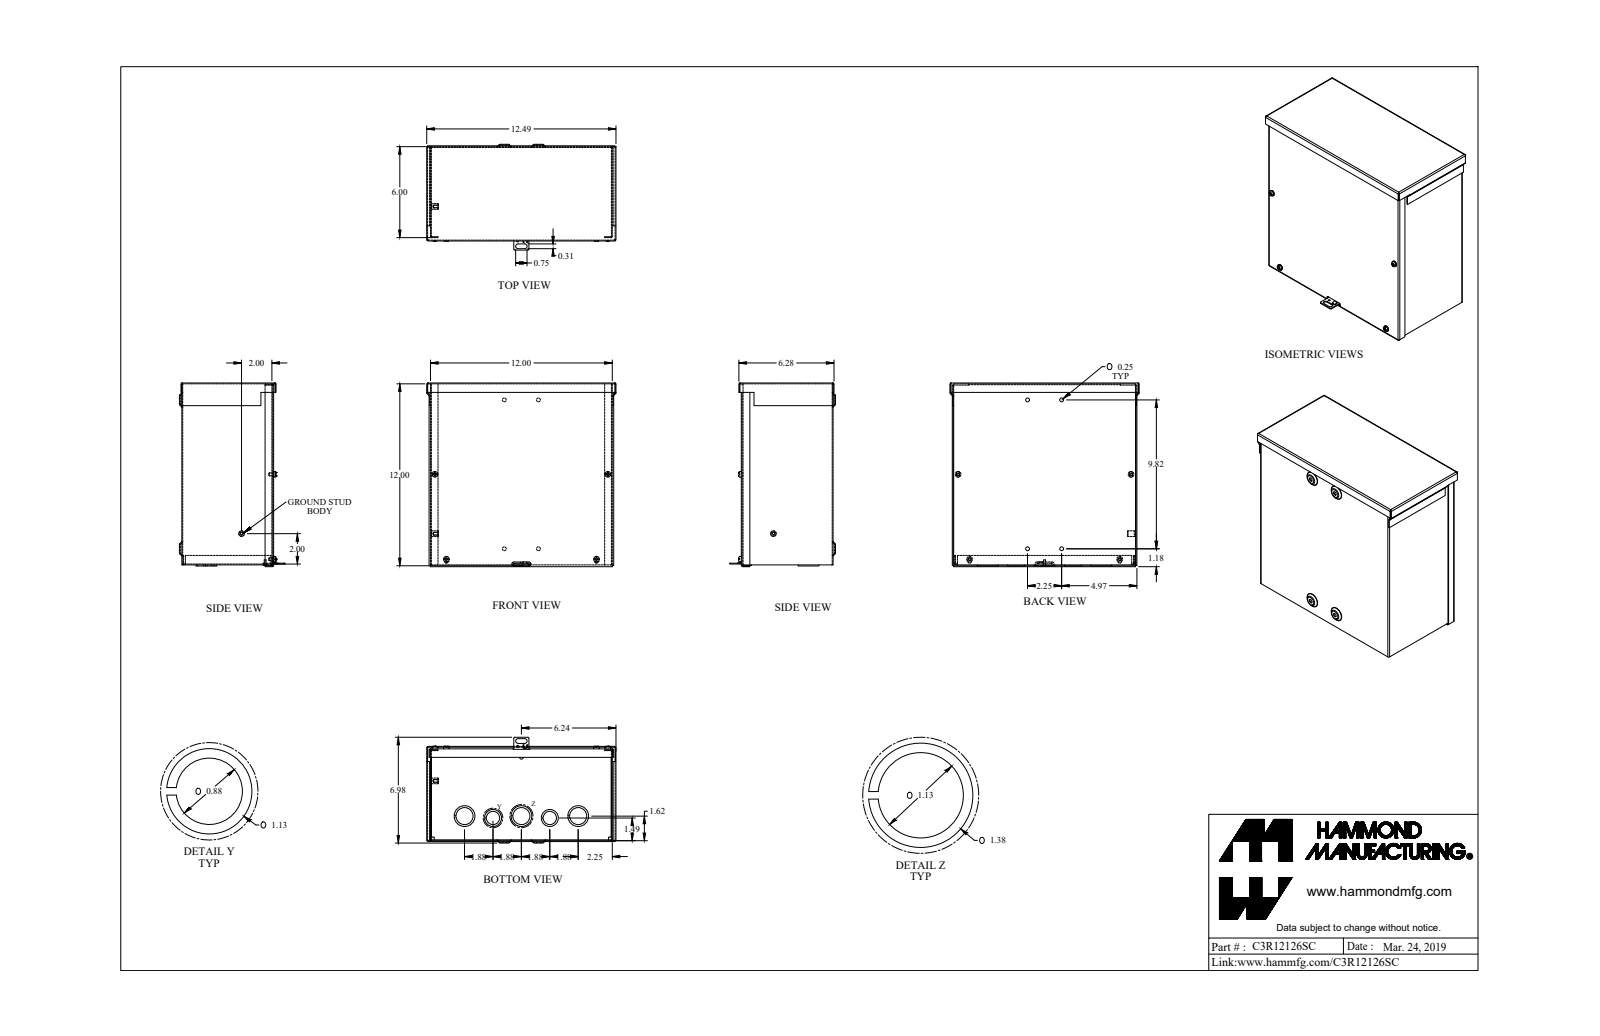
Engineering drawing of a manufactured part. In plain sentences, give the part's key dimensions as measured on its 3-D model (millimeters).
The part is named "C3R12126SC_Default". Its 3-D file was written by "SolidWorks 2019 (CONFIG_CONTROL_DESIGN)". It is 11 solids with 429 faces: 226 planar, 117 cylindrical and 86 other. Overall it measures 317.2 by 307.8 by 177.2 millimeters. Its volume is 620 900 cubic millimeters and its surface area 863 900 square millimeters. Round holes: 4 of diameter 4.3, 4 of diameter 6.4, 3 of diameter 28.6, 2 of diameter 22.2, 1 of diameter 3.2, 1 of diameter 3.5, 1 of diameter 4. Round bosses or shafts: 4 of diameter 4.8, 3 of diameter 9.5, 2 of diameter 34.9, 2 of diameter 28.6, 2 of diameter 9.5, 1 of diameter 34.9, 1 of diameter 3.2. Partial cylindrical surfaces (rounded edges, fillets, slot ends): 21 of radius 0.7, 21 of radius 2.2, 8 of radius 2.8, 8 of radius 3.2, 2 of radius 4. The main face-to-face distances are 1.4, 152.4, 303.4, 151, 153.8, 304.8, 1.4, 301.9, 301.9, 303.4. The hole center spacings are 170.6, 213.7, 95.3, 47.7, 47.8, 57.2, 99.6, 137.1.
